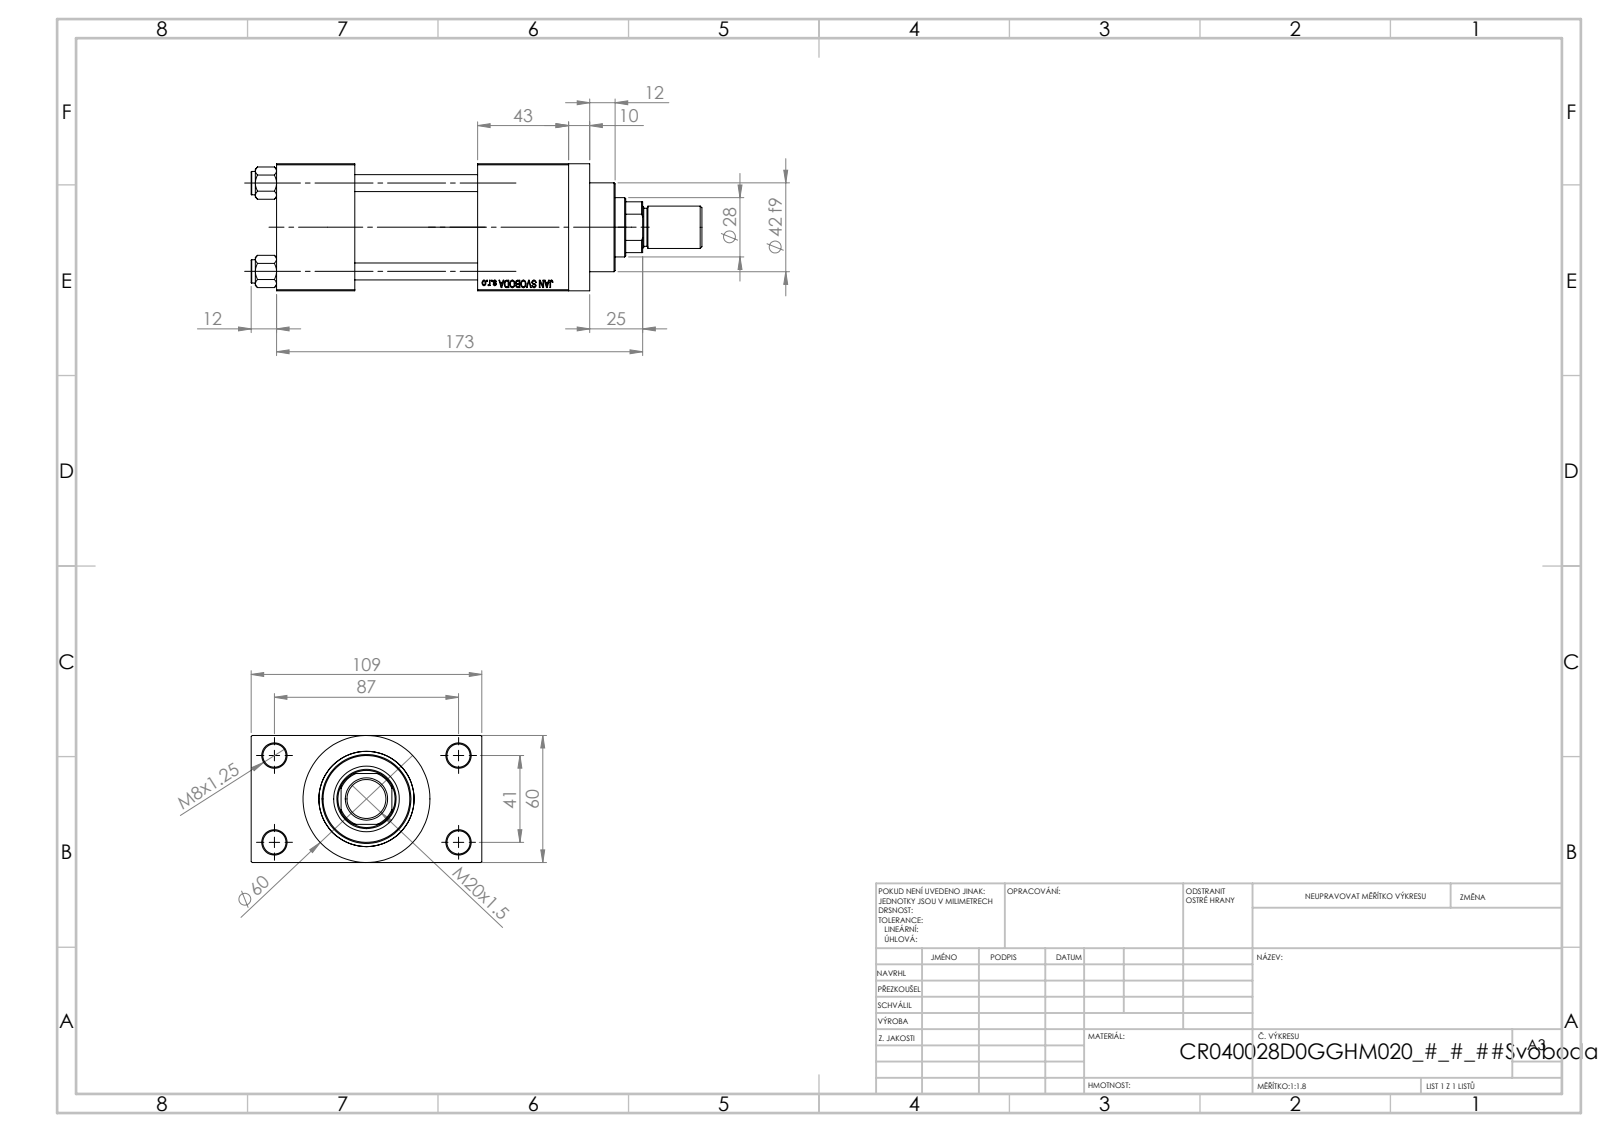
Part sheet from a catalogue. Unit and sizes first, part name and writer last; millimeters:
Units: millimetres
Overall size (bounding box): 213 × 109 × 60
Round holes (diameter × count): ⌀8 ×4, ⌀11 ×4, ⌀7 ×2, ⌀16.66 ×2, ⌀24 ×2, ⌀18.5 ×1, ⌀28 ×1, ⌀31 ×1, ⌀40 ×1, ⌀45 ×1
Round bosses / shafts (diameter × count): ⌀11 ×4, ⌀60 ×1, ⌀46 ×1, ⌀42 ×1, ⌀20 ×1, ⌀18 ×1
Partial cylindrical surfaces — rounded edges, fillets, slot ends (radius × count): R13.5 ×1
Main face-to-face distances: 60, 84.5, 24.5, 58, 37, 95, 138, 101, 43, 109
Hole centre spacings: 22.65, 29.49, 41.7, 47.15, 48.09, 64.35, 76.49, 41
Volume: 542 773 mm³ · Surface area: 130 260 mm²
Bodies: 12 solids, 1119 faces (502 planar, 93 cylindrical, 524 other)
Part name (STEP PRODUCT): ROD_END_AH; V215CR_VCP_D; V215CR_D_Body; V215_VC_A (+2 more)
STEP written by: SolidWorks 2019 (CONFIG_CONTROL_DESIGN)
